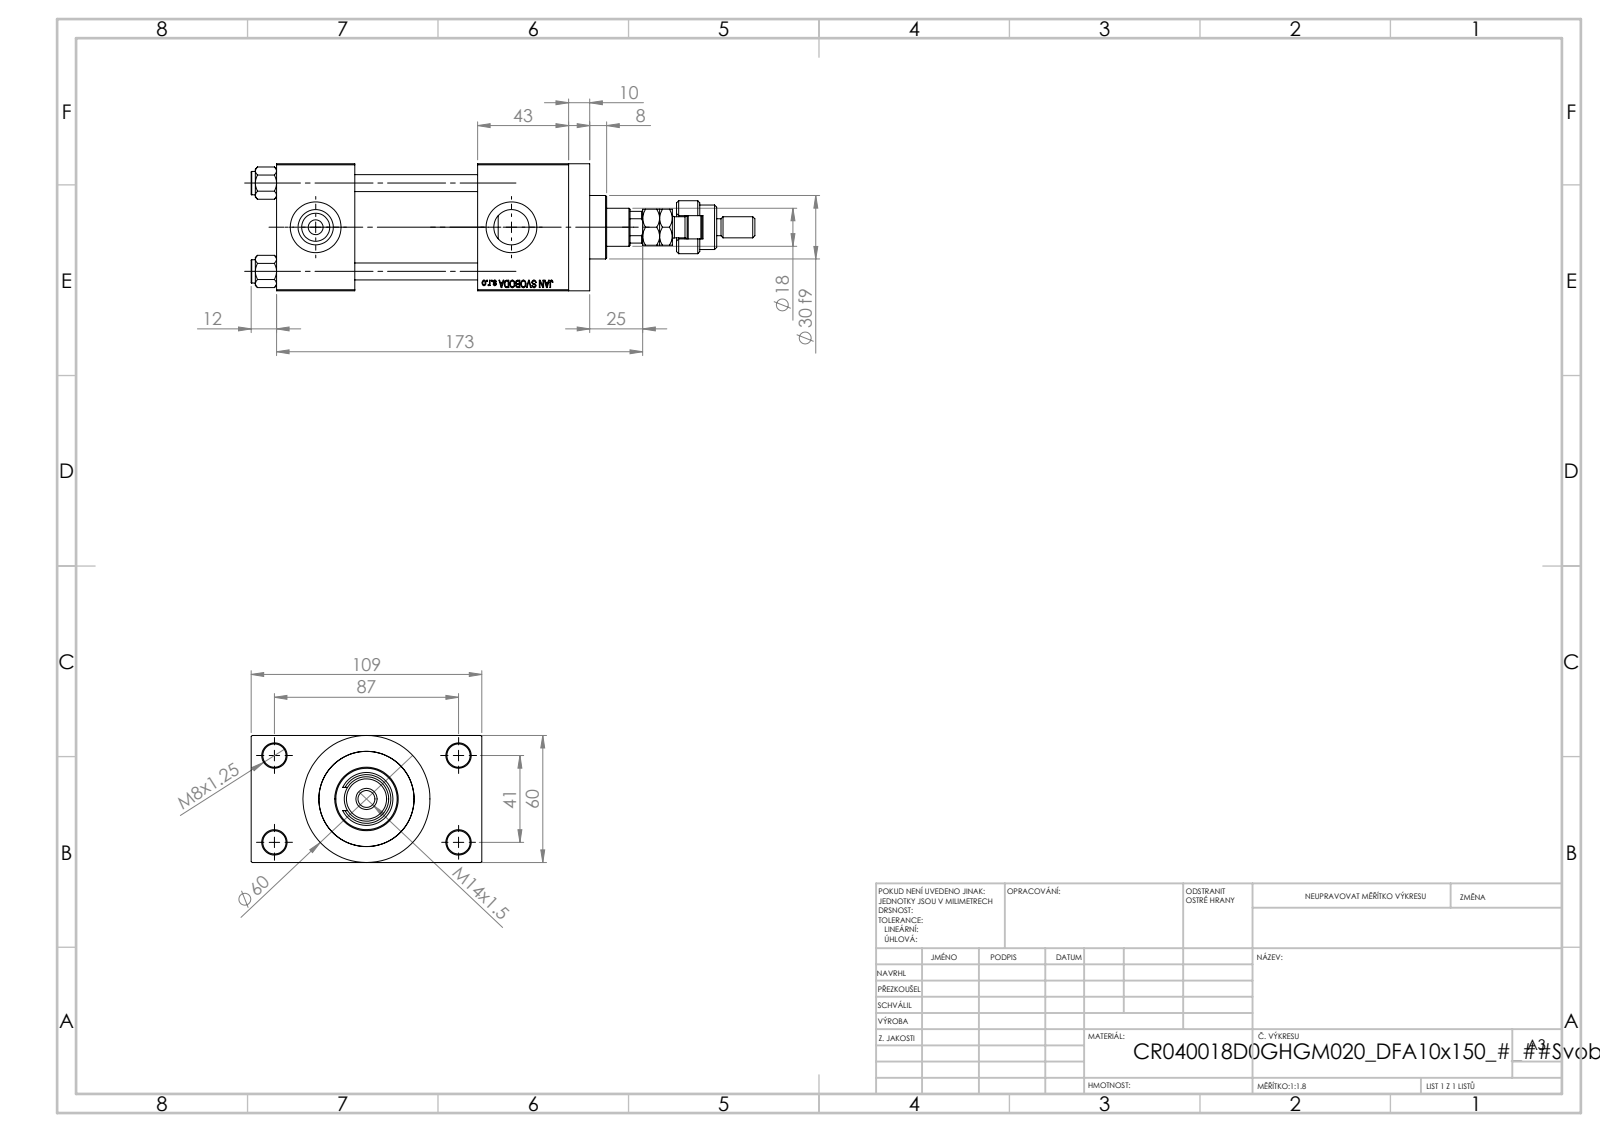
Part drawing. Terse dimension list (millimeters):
name: V215CR_D_Body; V215CR_VCP_D; V215CR_D_TYCINKA; MFA (+3 more)
written by: SolidWorks 2019 (CONFIG_CONTROL_DESIGN)
unit: mm
bodies: 13 solids, 1189 faces (526 planar, 101 cylindrical, 562 other)
size: 238 × 109 × 60
volume: 524 317 mm³; area: 127 992 mm²
holes: 4× ⌀8, 4× ⌀11, 2× ⌀7, 2× ⌀16.66, 2× ⌀24, 1× ⌀8.5, 1× ⌀18, 1× ⌀21, 1× ⌀31, 1× ⌀40, 1× ⌀45
bosses: 4× ⌀11, 1× ⌀60, 1× ⌀46, 1× ⌀30, 1× ⌀25, 1× ⌀16, 1× ⌀10, 1× ⌀8
rounds: 1× R5.5, 1× R8.5, 1× R8.75
face distances: 60, 24.5, 58, 84.5, 37, 95, 138, 101, 43, 53
hole spacings: 22.65, 29.49, 41.7, 47.15, 48.09, 64.35, 76.49, 41
